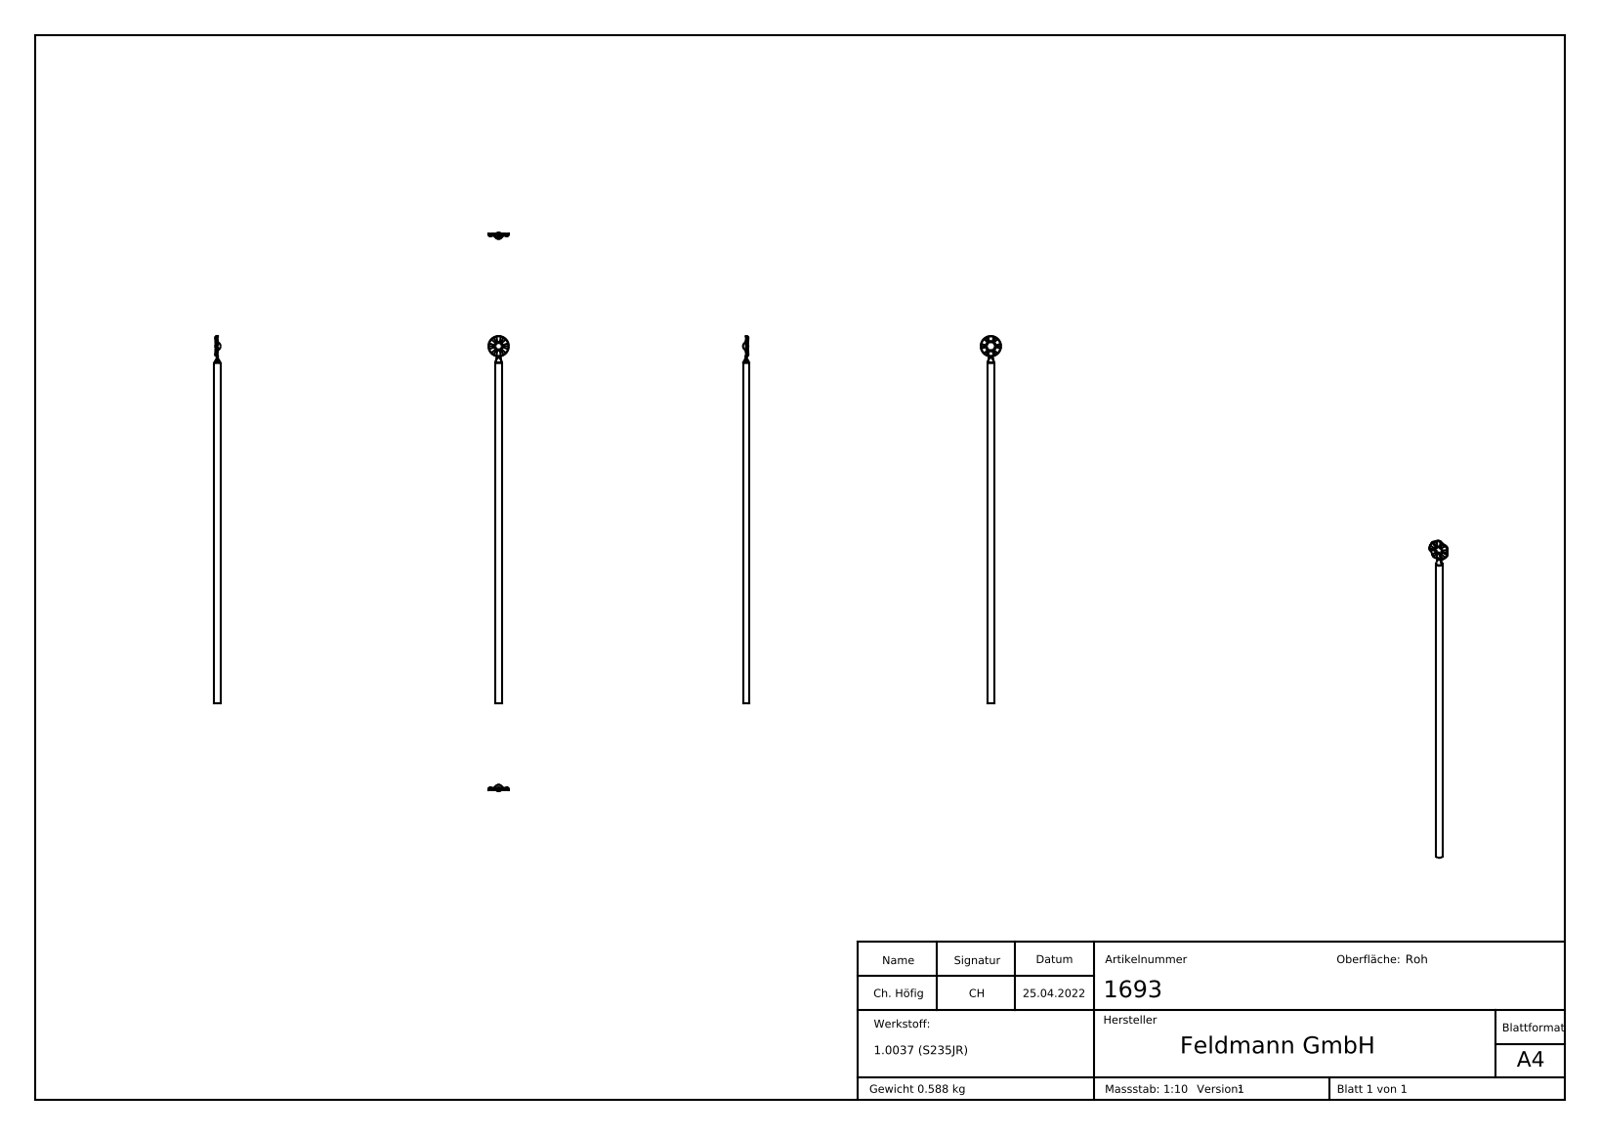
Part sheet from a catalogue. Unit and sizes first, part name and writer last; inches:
Units: inches
Overall size (bounding box): 27.165 × 1.496 × 0.472
Round bosses / shafts (diameter × count): ⌀1.496 ×1, ⌀0.472 ×1
Partial cylindrical surfaces — rounded edges, fillets, slot ends (radius × count): R0.008 ×4
Main face-to-face distances: 0.02, 0.018, 0.087, 0.022, 0.027, 0.057, 0.013, 0.064, 0.028, 0.161
Volume: 4.601 in³ · Surface area: 42.4 in²
Bodies: 1 solid, 382 faces (116 planar, 6 cylindrical, 260 other)
Part name (STEP PRODUCT): 1693
STEP written by: SolidWorks 2018 (CONFIG_CONTROL_DESIGN)
